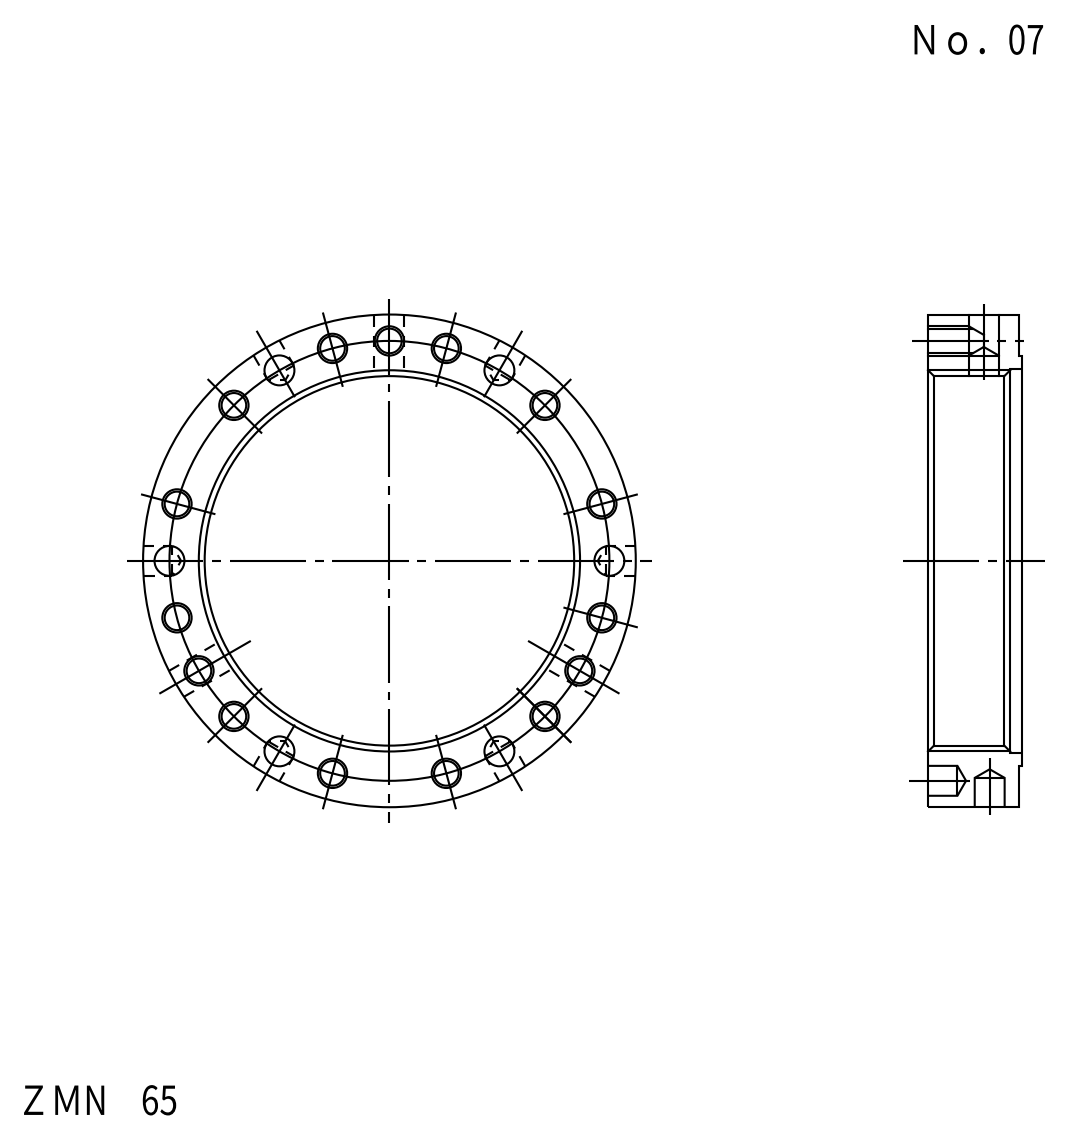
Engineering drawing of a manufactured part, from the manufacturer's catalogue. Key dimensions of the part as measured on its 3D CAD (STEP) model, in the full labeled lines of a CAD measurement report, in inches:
Part name (STEP PRODUCT): FKD ZMN65
STEP written by: Autodesk Inventor LT (CONFIG_CONTROL_DESIGN)
Units: inches
Bodies: 1 solid, 62 faces (4 planar, 34 cylindrical, 24 other)
Overall size (bounding box): 3.307 × 3.307 × 0.63
Volume: 1.877 in³ · Surface area: 23.31 in²
Round holes (diameter × count): ⌀0.163 ×15, ⌀0.201 ×12, ⌀2.559 ×1, ⌀2.579 ×1
Round bosses / shafts (diameter × count): ⌀3.307 ×1, ⌀2.756 ×1
Main face-to-face distances: 0.61, 0.02, 0.63, 0.059, 0.039, 0.571
Hole centre spacings: 1.476, 1.13, 2.557, 2.852, 0.385, 0.764, 1.798, 2.343
